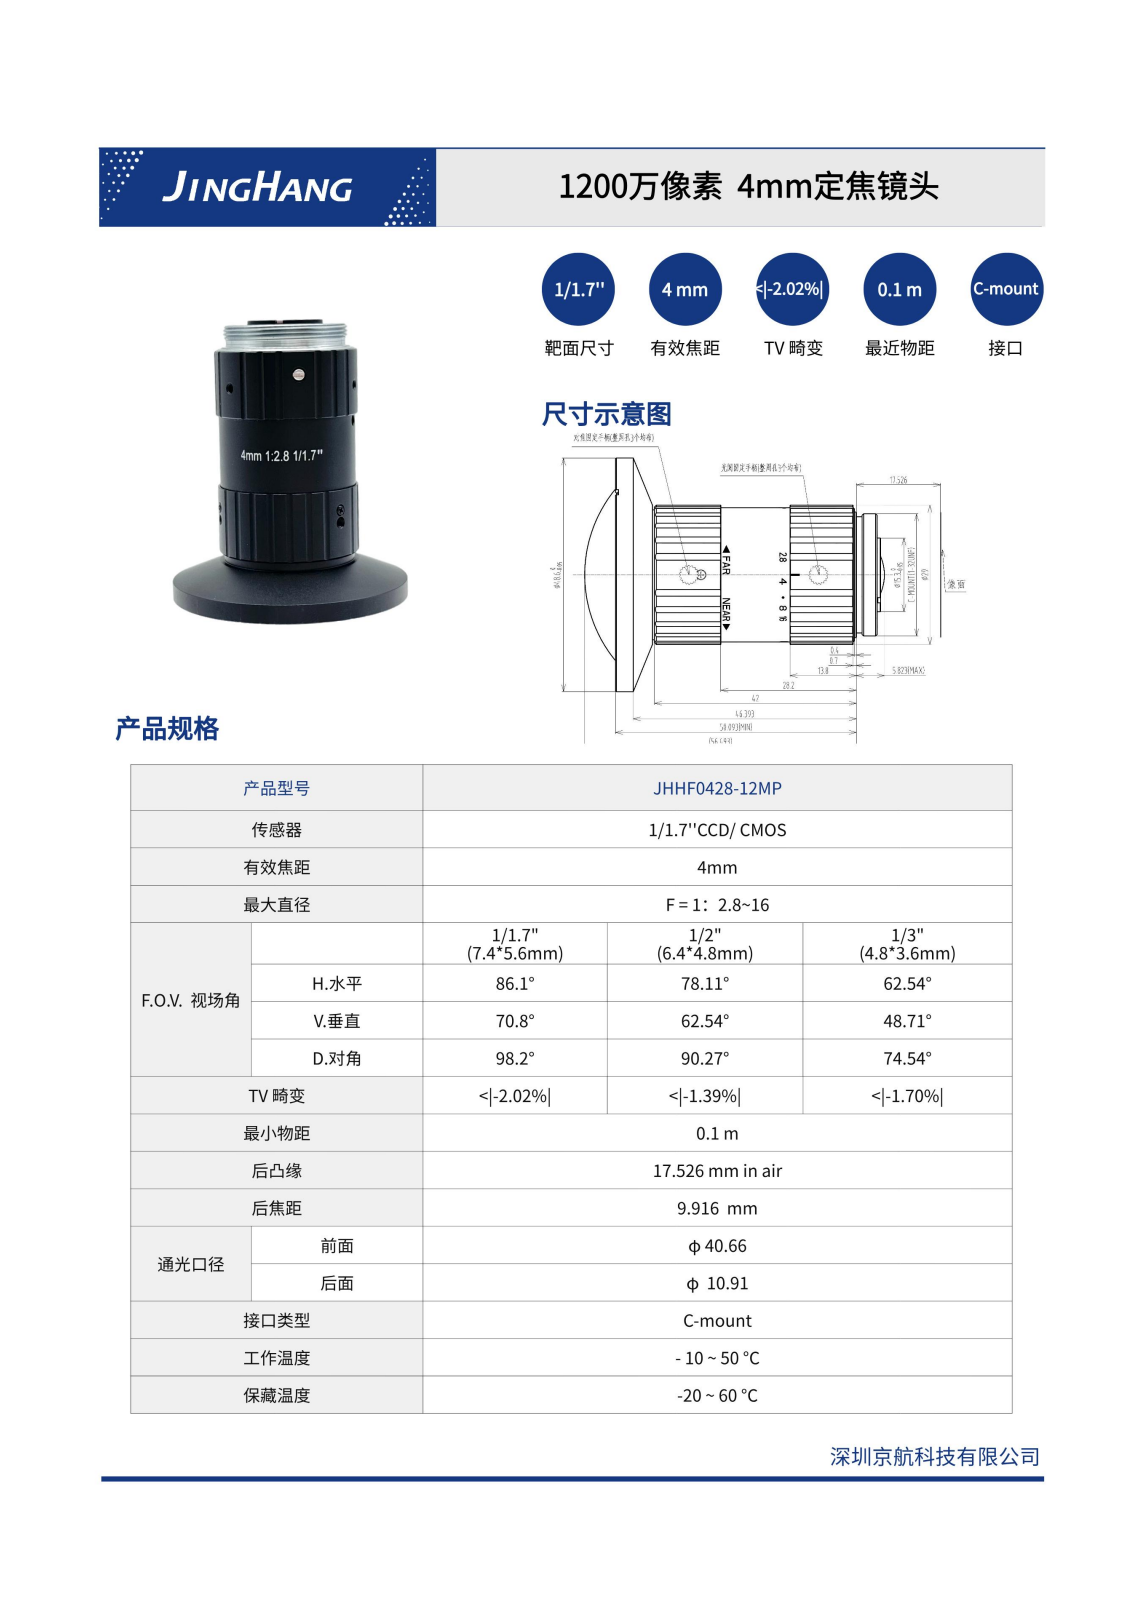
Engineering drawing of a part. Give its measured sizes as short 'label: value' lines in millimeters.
name: GB1524A-504_AF0; GB1524A-502_AF0; GB1524A-307_AF0; GB1524A-513_AF0 (+8 more)
written by: CREO PARAMETRIC BY PTC INC, 2022073 (CONFIG_CONTROL_DESIGN)
unit: mm
bodies: 25 solids, 1561 faces (513 planar, 462 cylindrical, 586 other)
size: 62.31 × 48.6 × 48.6
volume: 12 505 mm³; area: 24 060 mm²
holes: 10× ⌀1.4, 9× ⌀1.6, 8× ⌀2, 4× ⌀1.5, 4× ⌀1.7, 4× ⌀2.1, 3× ⌀1.25, 3× ⌀2.6, 1× ⌀1.3, 1× ⌀2.7, 1× ⌀11, 1× ⌀11.8
bosses: 6× ⌀2.5, 5× ⌀2, 4× ⌀1.08, 3× ⌀1.6, 2× ⌀1.5, 1× ⌀48.6, 1× ⌀47, 1× ⌀27.9
rounds: 41× R1.5, 12× R0.3, 4× R2, 2× R0.85, 1× R7.5, 1× R14.5
face distances: 49.88, 41.94, 41.65, 49.59, 7.94, 2, 15.6, 3.4, 51.88, 51.59
hole spacings: 2.5, 16.88, 0.57, 9.74, 9.75, 16.59, 16.89, 17.16
